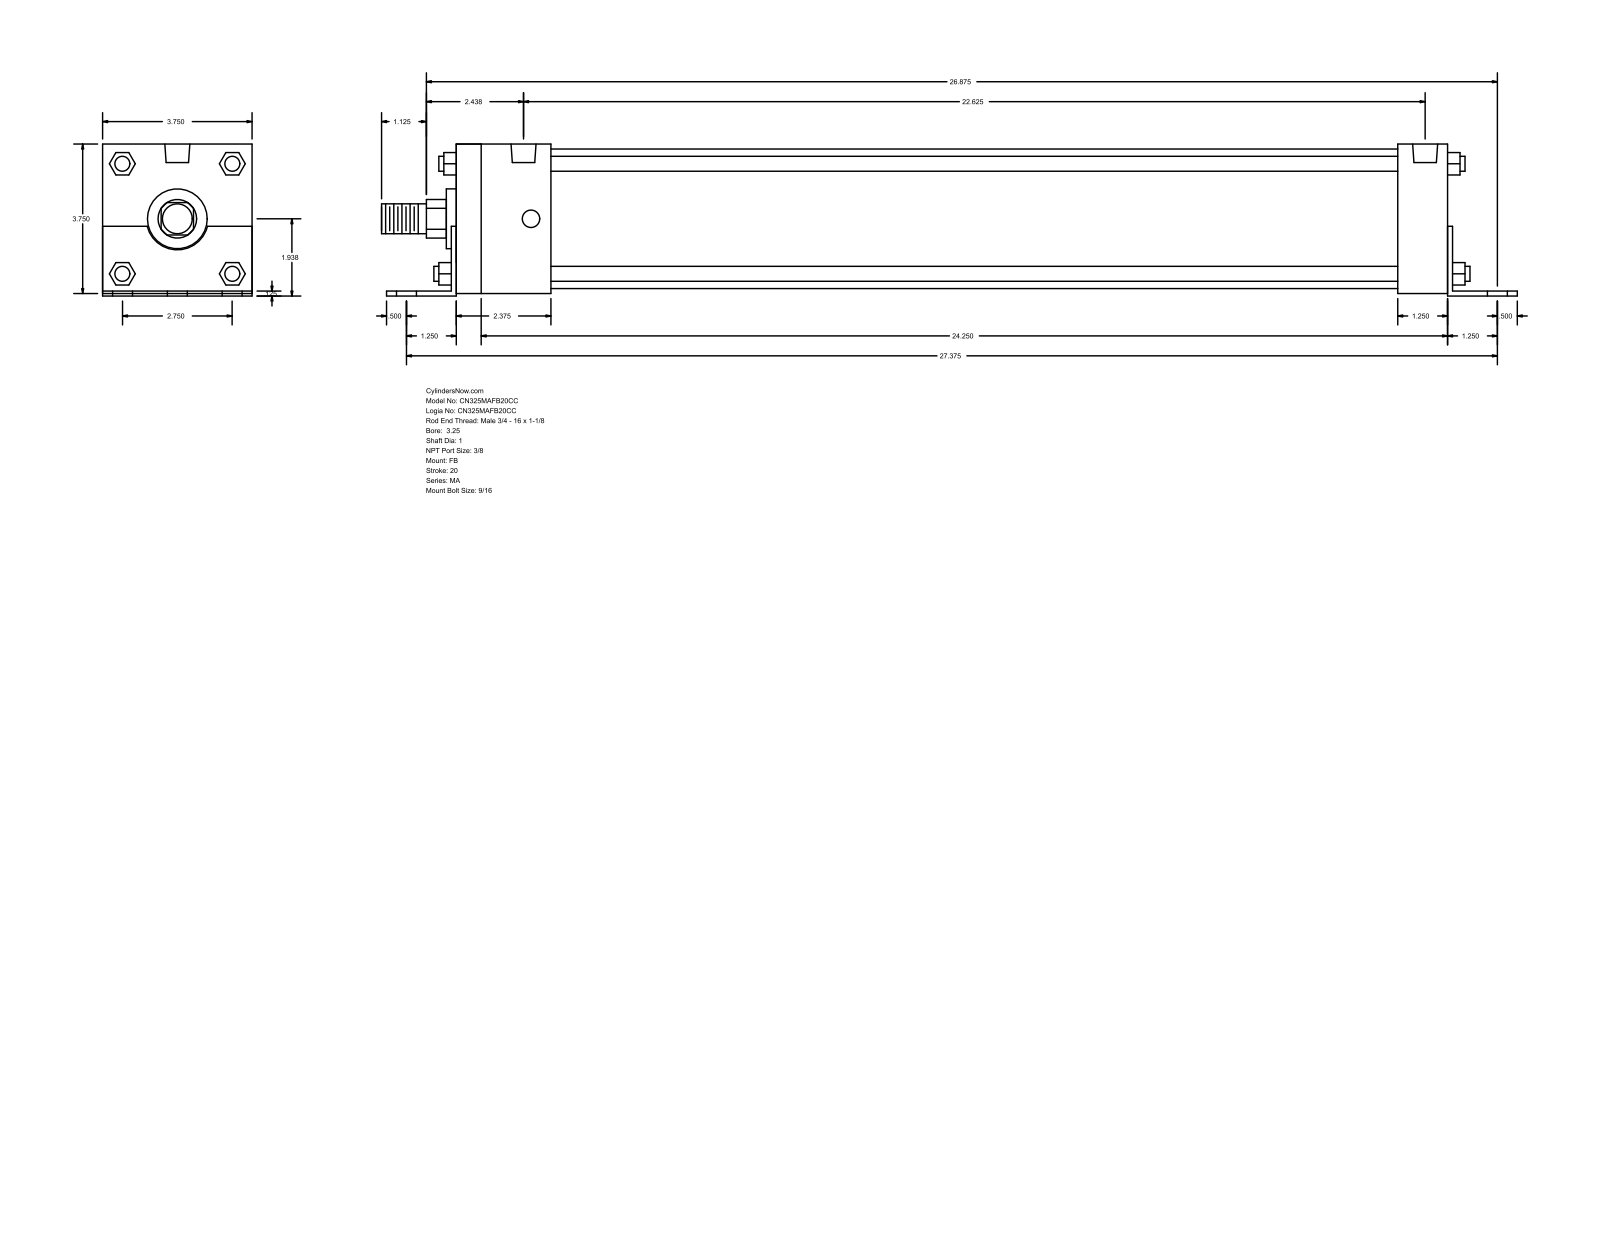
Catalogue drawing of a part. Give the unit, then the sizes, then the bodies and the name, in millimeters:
Units: millimetres
Overall size (bounding box): 723.9 × 96.84 × 95.25
Round holes (diameter × count): ⌀14.29 ×6, ⌀11.11 ×4, ⌀15.93 ×2
Round bosses / shafts (diameter × count): ⌀9.53 ×4, ⌀88.9 ×1, ⌀38.1 ×1, ⌀25.4 ×1, ⌀19.05 ×1
Partial cylindrical surfaces — rounded edges, fillets, slot ends (radius × count): R12.29 ×1, R19.81 ×1
Main face-to-face distances: 95.24, 3.17, 1.59, 96.83, 1.58, 93.66, 635, 631.83, 638.17, 34.93
Hole centre spacings: 34.92, 696.2, 695.32, 4.76, 57.78, 61.64, 69.84, 82.38
Bodies: 0 solids, 140 faces (105 planar, 35 cylindrical, 0 other)
Part name (STEP PRODUCT): MA_FB__0325_1
STEP written by: GSSL Pune (CONFIG_CONTROL_DESIGN)
